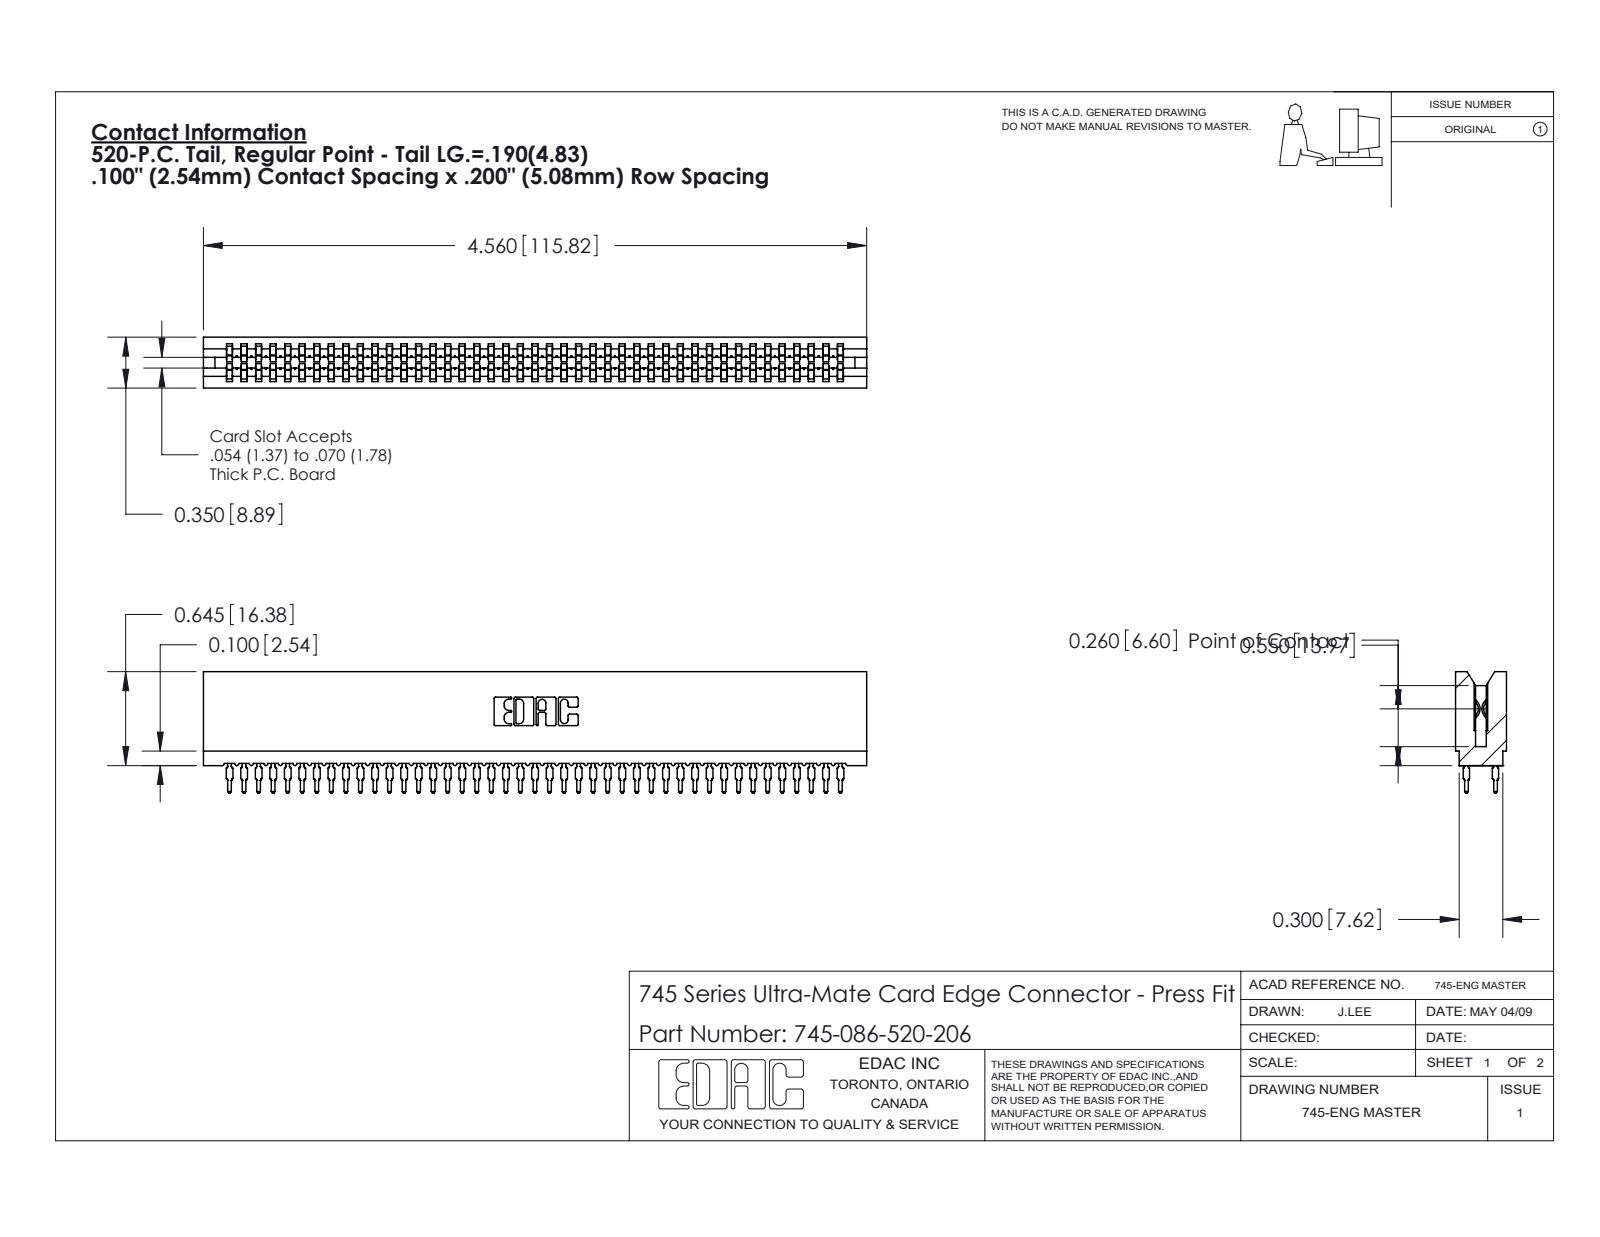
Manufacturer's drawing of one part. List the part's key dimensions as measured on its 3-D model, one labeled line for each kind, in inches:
Part name (STEP PRODUCT): 745-086-520-206; 745-292-001_520; 745 Part_Insulator Option - 06
STEP written by: SolidWorks 2020 (CONFIG_CONTROL_DESIGN)
Units: inches
Bodies: 87 solids, 7793 faces (4012 planar, 1545 cylindrical, 2236 other)
Overall size (bounding box): 4.56 × 0.836 × 0.35
Volume: 0.63 in³ · Surface area: 32.01 in²
Partial cylindrical surfaces — rounded edges, fillets, slot ends (radius × count): R0.021 ×172, R0.015 ×86, R0.01 ×22, R0.005 ×8, R0.011 ×8, R0.007 ×6, R0.031 ×6, R0.026 ×3
Main face-to-face distances: 0.35, 0.063, 0.287, 0.045, 0.305, 0.018, 0.243, 0.138, 0.212, 0.093
